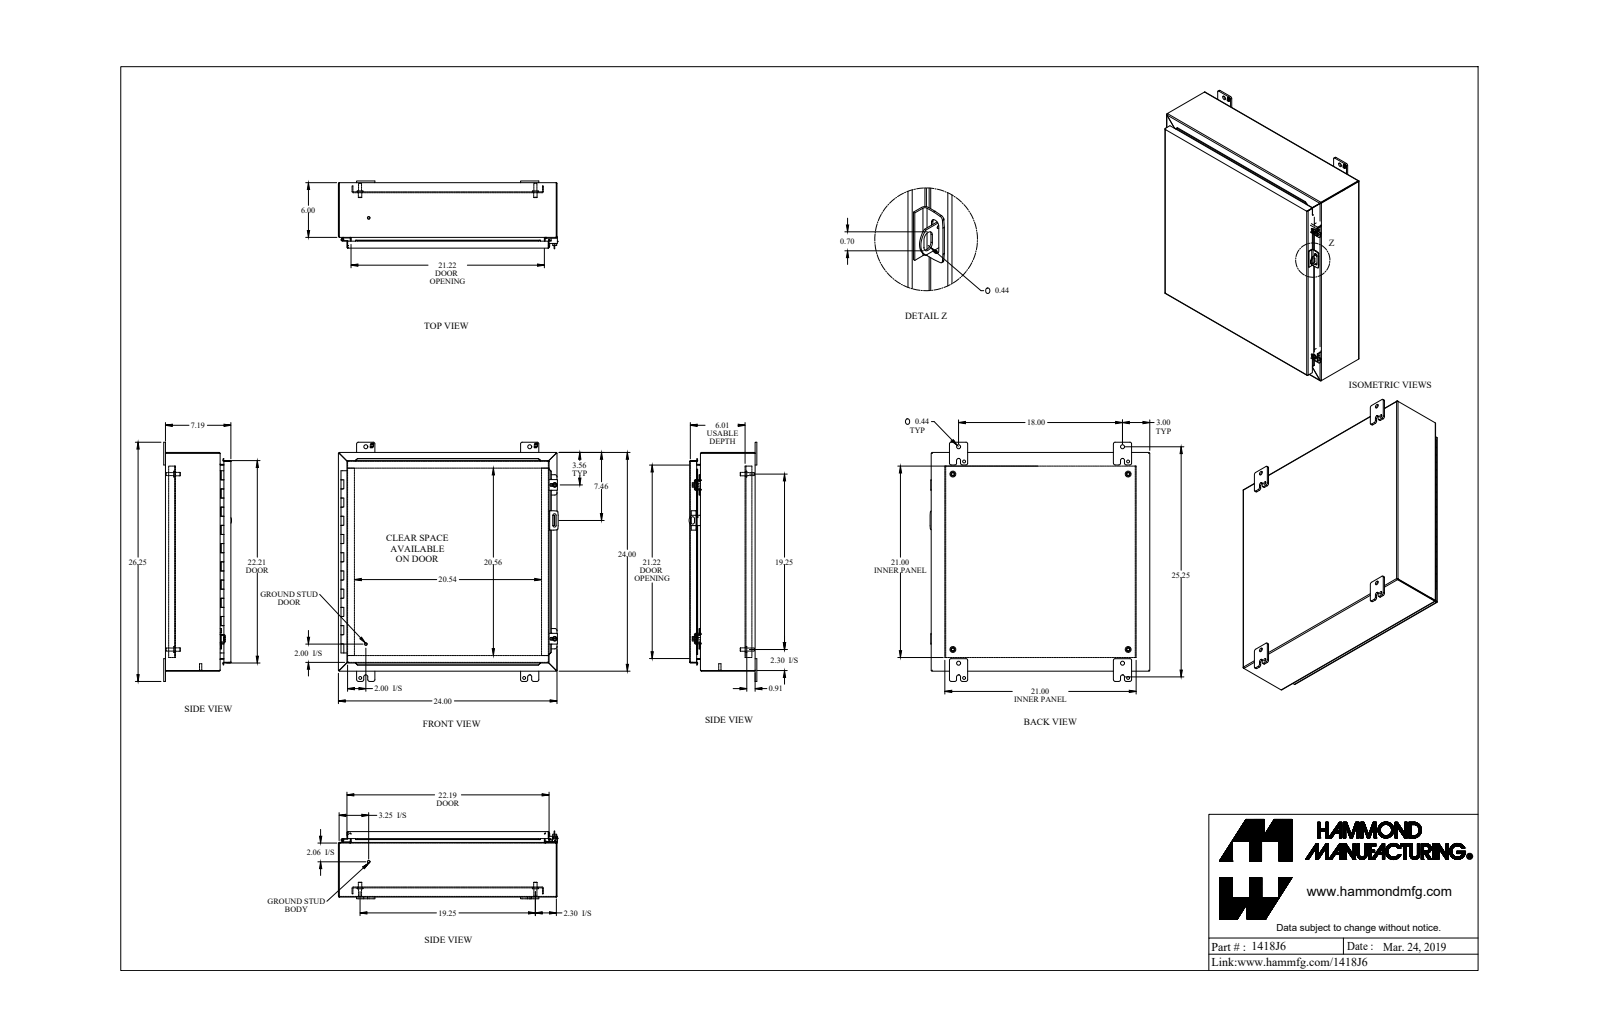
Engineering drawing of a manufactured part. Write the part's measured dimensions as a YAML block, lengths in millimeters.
part_name: "1418J6"
step_written_by: "SolidWorks 2019 (AUTOMOTIVE_DESIGN)"
units: millimeters
bodies: {solids: 38, faces: 1004, planar: 687, cylindrical: 263, other: 54}
overall_size: [666.8, 612.8, 188.9]
volume: 3354000
surface_area: 3401000
round_holes:
  - {diameter: 8, count: 4}
  - {diameter: 11.1, count: 4}
  - {diameter: 12.7, count: 4}
  - {diameter: 5.4, count: 2}
  - {diameter: 6.7, count: 2}
  - {diameter: 7.8, count: 2}
  - {diameter: 9.5, count: 2}
  - {diameter: 3.2, count: 1}
  - {diameter: 4.7, count: 1}
  - {diameter: 11.3, count: 1}
  - {diameter: 11.3, count: 1}
round_bosses_or_shafts:
  - {diameter: 16.5, count: 4}
  - {diameter: 9.5, count: 4}
  - {diameter: 8.4, count: 4}
  - {diameter: 25.4, count: 2}
  - {diameter: 12.7, count: 2}
  - {diameter: 9.9, count: 2}
  - {diameter: 7.1, count: 2}
  - {diameter: 6.4, count: 2}
partial_cylinders:
  - {radius: 4.8, count: 26}
  - {radius: 0.9, count: 20}
  - {radius: 2.7, count: 20}
  - {radius: 1.2, count: 13}
  - {radius: 3.6, count: 13}
  - {radius: 0.2, count: 8}
  - {radius: 1.1, count: 8}
  - {radius: 2, count: 8}
face_to_face_distances: [1.8, 180.7, 178.8, 607.8, 182.5, 23.8, 2.4, 25.6, 154.5, 152.6]
hole_center_spacings: [489, 457.2, 44.1, 77.9, 489, 527.3, 603.3, 691.5]
